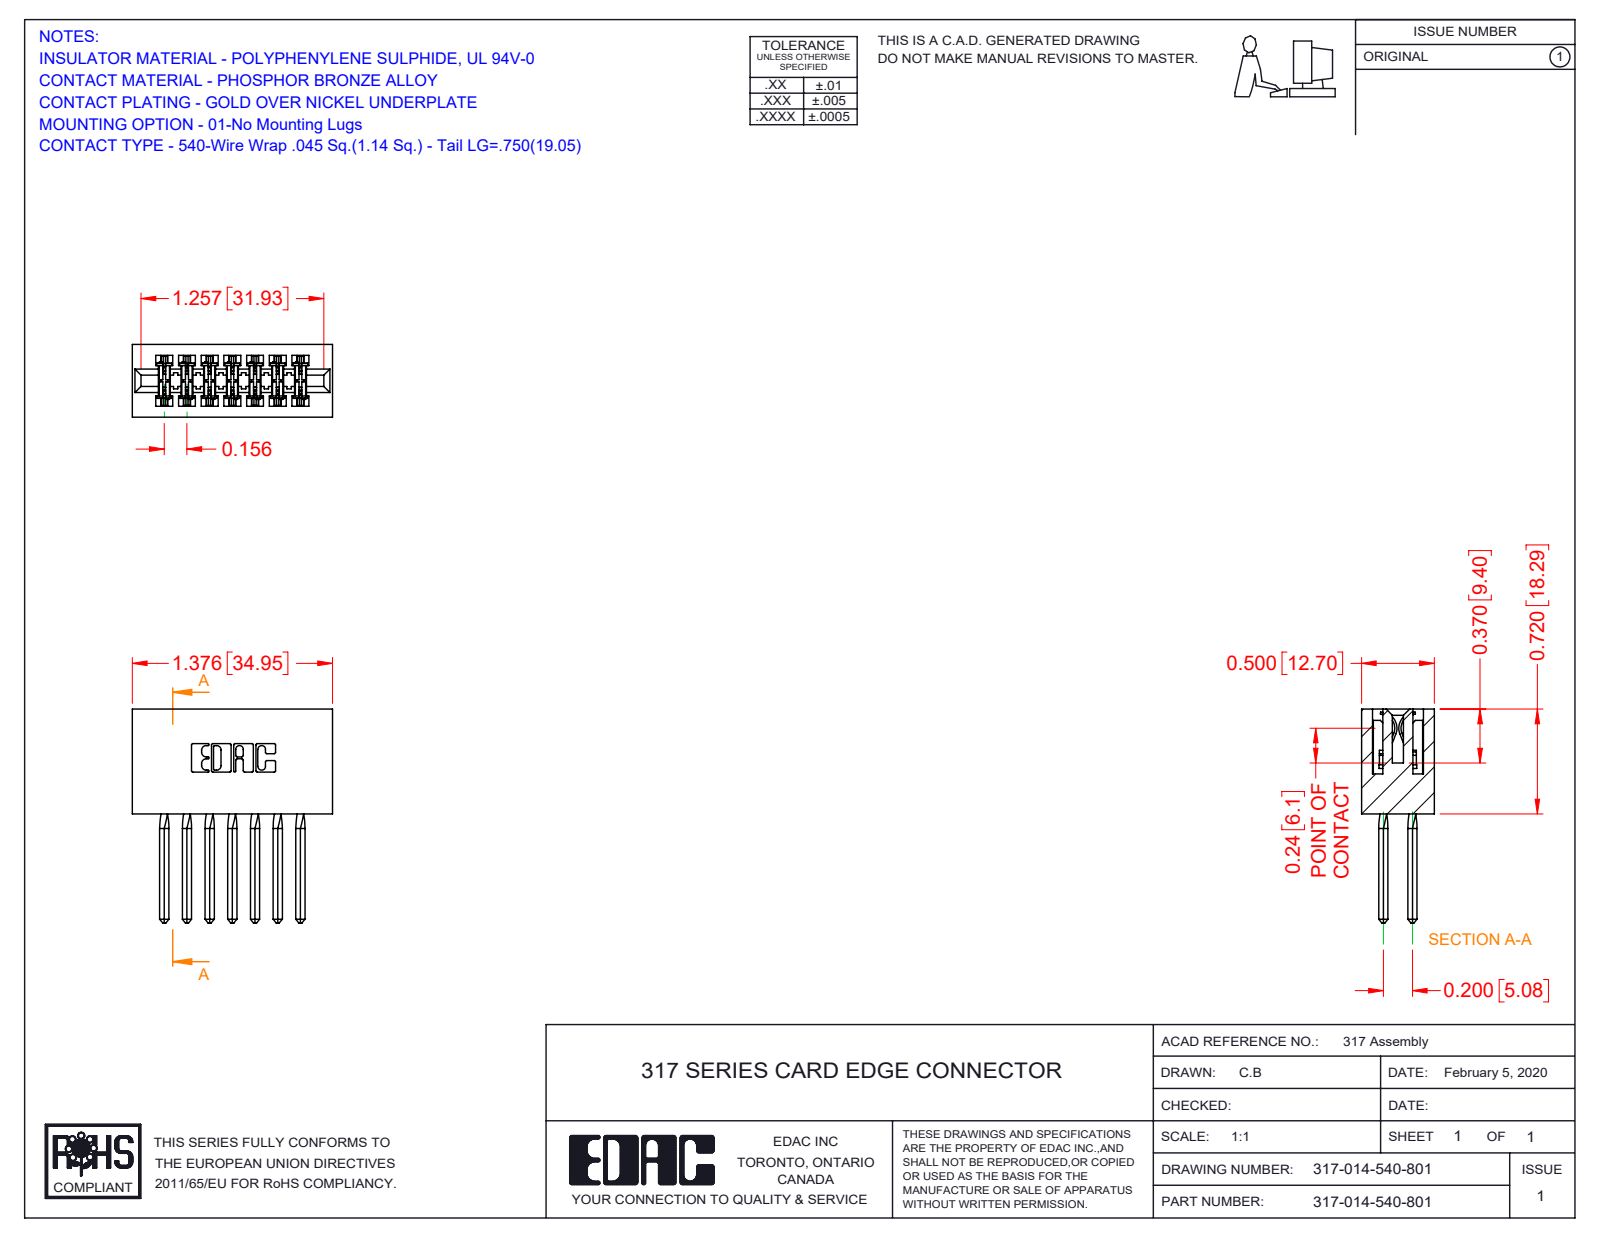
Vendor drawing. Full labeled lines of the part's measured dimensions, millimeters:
Part name (STEP PRODUCT): 317 Part_Lugless; 317-290-001_540; 317-014-540-801
STEP written by: SolidWorks 2016 (CONFIG_CONTROL_DESIGN)
Units: millimetres
Bodies: 15 solids, 1336 faces (1072 planar, 208 cylindrical, 56 other)
Overall size (bounding box): 37.3 × 35 × 12.7
Volume: 6 470 mm³ · Surface area: 8 587 mm²
Partial cylindrical surfaces — rounded edges, fillets, slot ends (radius × count): R0.4 ×28, R0.3 ×22, R0.2 ×6, R0.8 ×6, R0.7 ×3, R2.4 ×2, R2.5 ×2, R2.8 ×2
Main face-to-face distances: 12.7, 2.8, 1.9, 10.8, 4, 5.6, 2.9, 1.7, 8.4, 3.5
